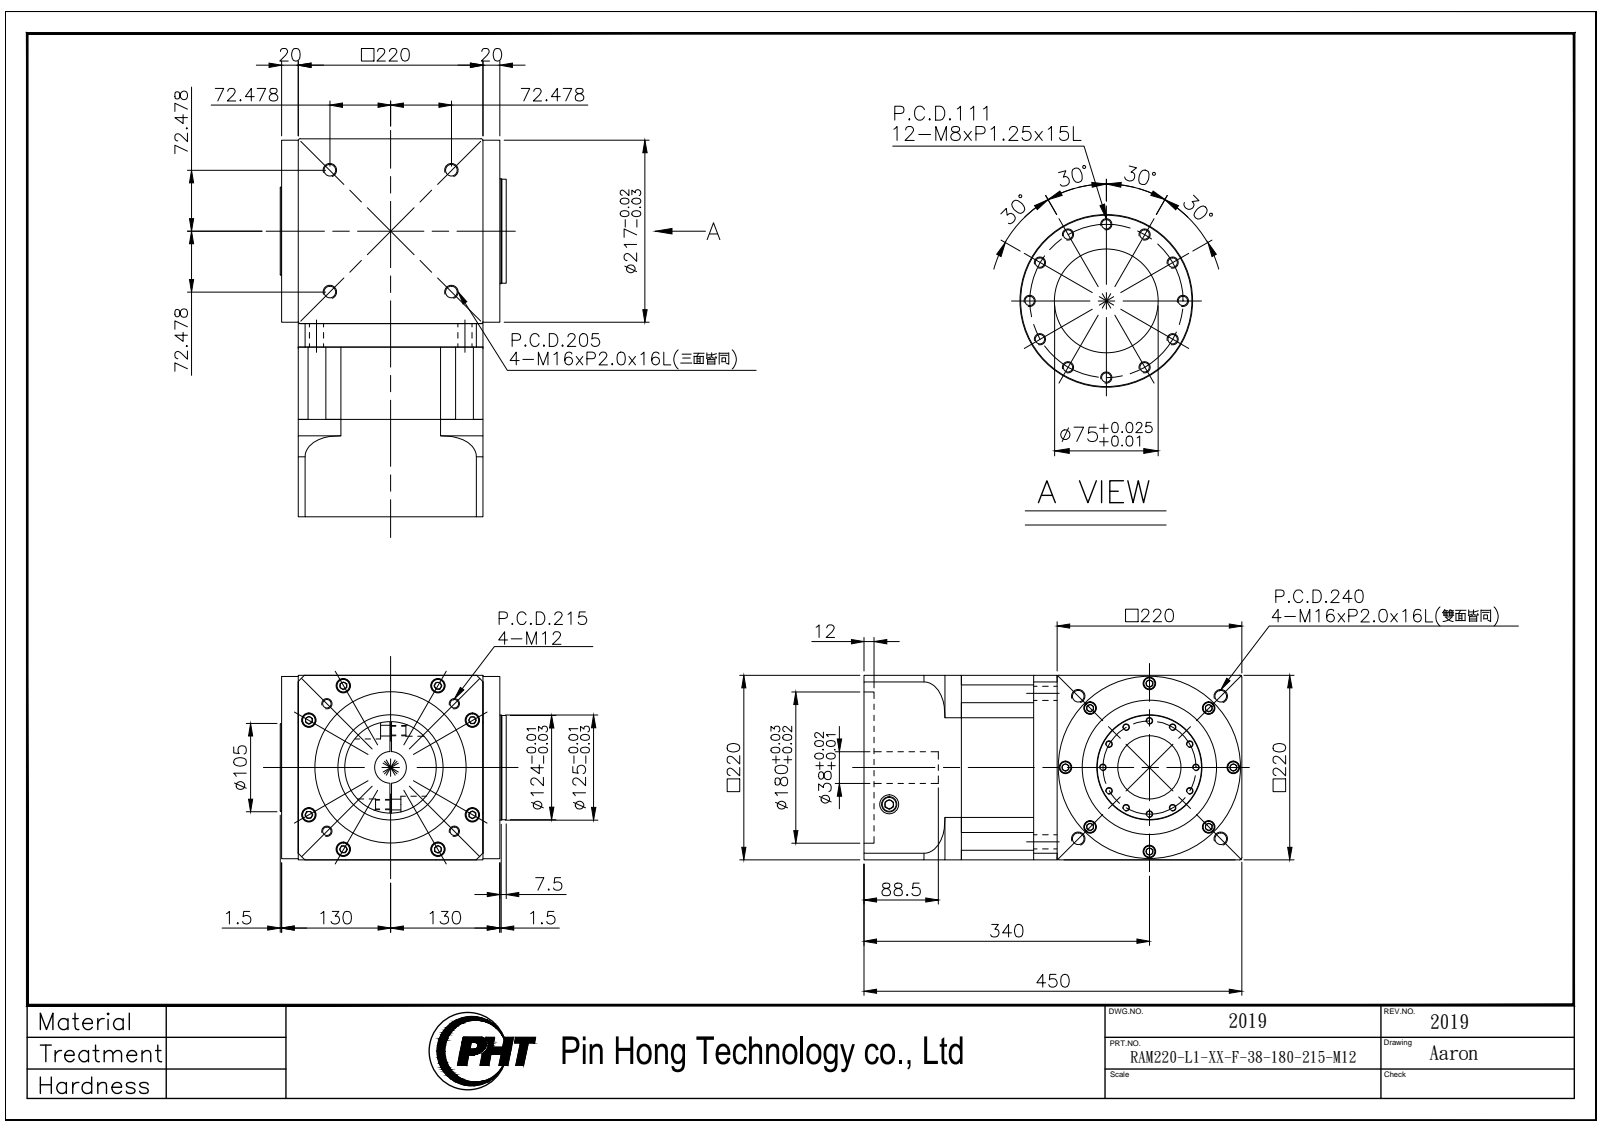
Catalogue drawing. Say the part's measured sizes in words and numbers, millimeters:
The part is named "RAM220-L1-XX-F-38-180-215-M12_2019". Its 3-D file was written by "SolidWorks 2016 (AUTOMOTIVE_DESIGN)". It is 4 solids with 996 faces: 440 planar, 342 cylindrical and 214 other. Overall it measures 450 by 269 by 220 millimeters. Its volume is 21 010 000 cubic millimeters and its surface area 1 057 000 square millimeters. Round holes: 12 of diameter 6.8, 12 of diameter 9, 12 of diameter 14, 12 of diameter 15, 12 of diameter 17, 8 of diameter 11, 4 of diameter 10.2, 2 of diameter 22.5, 1 of diameter 38, 1 of diameter 75, 1 of diameter 75.6, 1 of diameter 125. Round bosses or shafts: 12 of diameter 13, 8 of diameter 16, 4 of diameter 24, 1 of diameter 217, 1 of diameter 160, 1 of diameter 125, 1 of diameter 124, 1 of diameter 120. Partial cylindrical surfaces (rounded edges, fillets, slot ends): 4 of radius 15, 1 of radius 125, 1 of radius 150. The main face-to-face distances are 220, 86, 114, 28, 334, 248, 20, 240, 129, 43. The hole center spacings are 55.5, 100, 136.49, 150.64, 58.88, 86.77, 114.37, 44.5.
